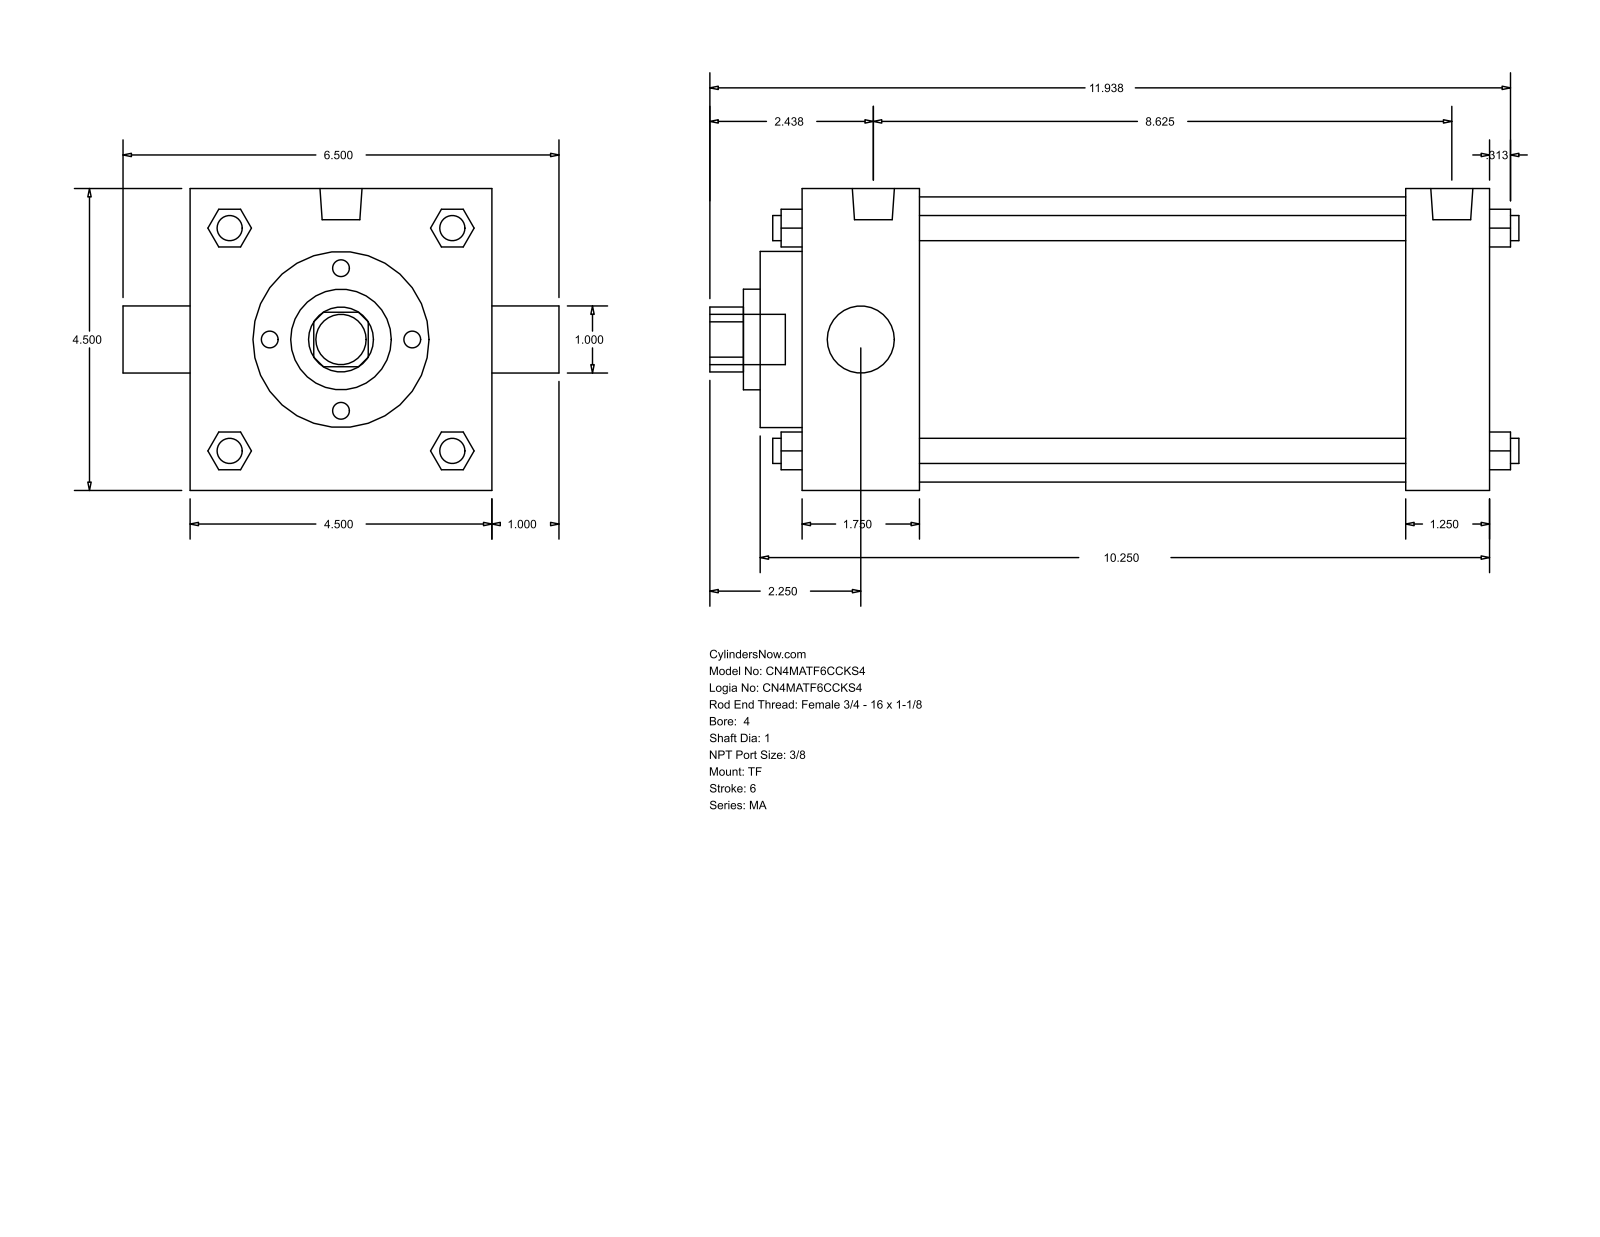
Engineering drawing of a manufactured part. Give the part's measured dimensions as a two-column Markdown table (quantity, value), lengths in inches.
| quantity | value |
| --- | --- |
| part name | MA_TF__0400_1 |
| STEP written by | GSSL Pune (CONFIG_CONTROL_DESIGN) |
| units | inches |
| bodies | 0 solids, 122 faces (93 planar, 29 cylindrical, 0 other) |
| overall size | 12.063 × 6.5 × 4.5 |
| round holes (diameter × count) | 1 × 2, 1.5 × 1, 2.625 × 1, 4.25 × 1 |
| round bosses / shafts (diameter × count) | 0.375 × 4, 0.437 × 3, 0.627 × 2, 0.75 × 1 |
| partial cylindrical surfaces (radius × count) | 0.484 × 1 |
| main face-to-face distances | 4.5, 10.25, 9, 1.25, 1.75, 7.25, 8.5, 10.875, 0.625, 2.375 |
